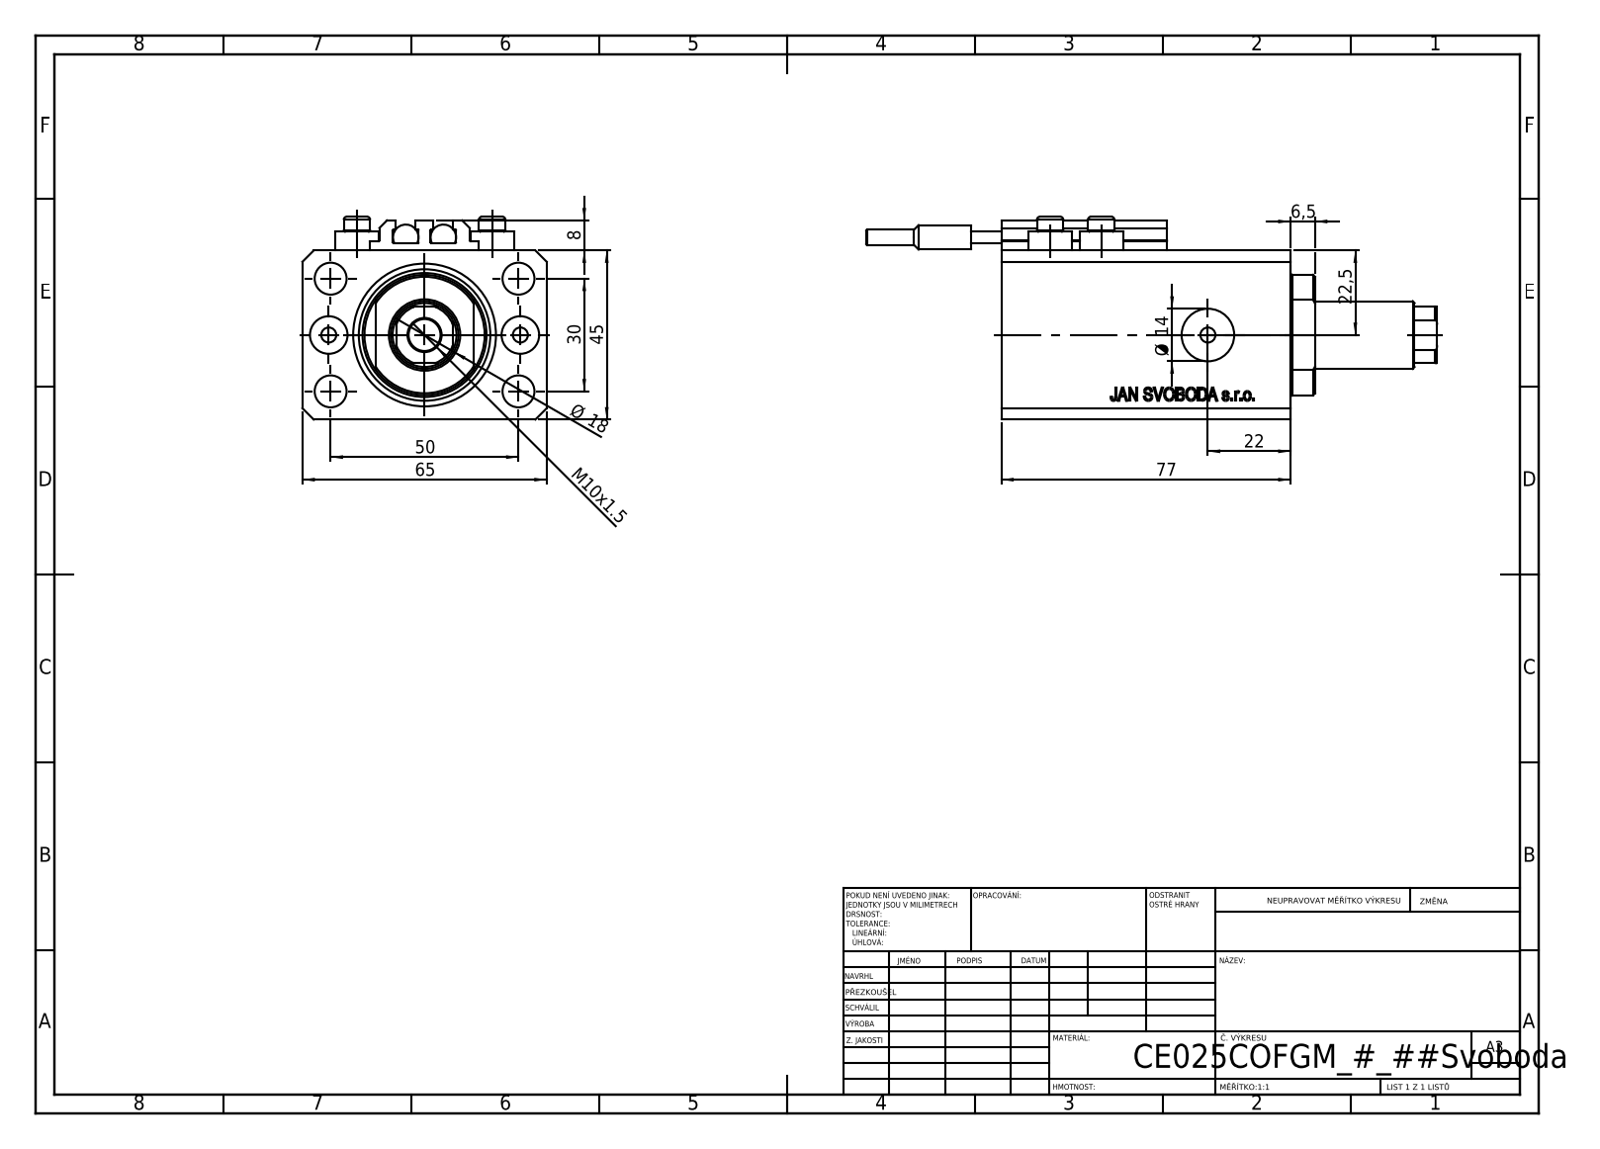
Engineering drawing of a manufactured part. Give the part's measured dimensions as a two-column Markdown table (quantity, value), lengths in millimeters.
| quantity | value |
| --- | --- |
| part name | V250CE_C_Body; SWITCH_V250CE; ALLEN BOLT V250CE; V250CE_C_VCP (+1 more) |
| STEP written by | SolidWorks 2019 (CONFIG_CONTROL_DESIGN) |
| units | millimeters |
| bodies | 10 solids, 1087 faces (537 planar, 98 cylindrical, 452 other) |
| overall size | 152 × 65 × 54 |
| volume | 227 732 mm³ |
| surface area | 60 300 mm² |
| round holes (diameter × count) | 4 × 8, 8.5 × 5, 10 × 2, 14 × 2, 18 × 1, 25 × 1, 38 × 1 |
| round bosses / shafts (diameter × count) | 11.6 × 4, 7 × 4, 6.8 × 2, 6.5 × 2, 4 × 2 |
| partial cylindrical surfaces (radius × count) | 0.2 × 10, 8.5 × 1, 16 × 1 |
| main face-to-face distances | 45, 65, 51.9, 77, 25.1, 3, 32, 47, 19.9, 2 |
| hole center spacings | 15.01, 29.15, 52.68, 13.6, 25.5, 30, 36, 38.48 |
